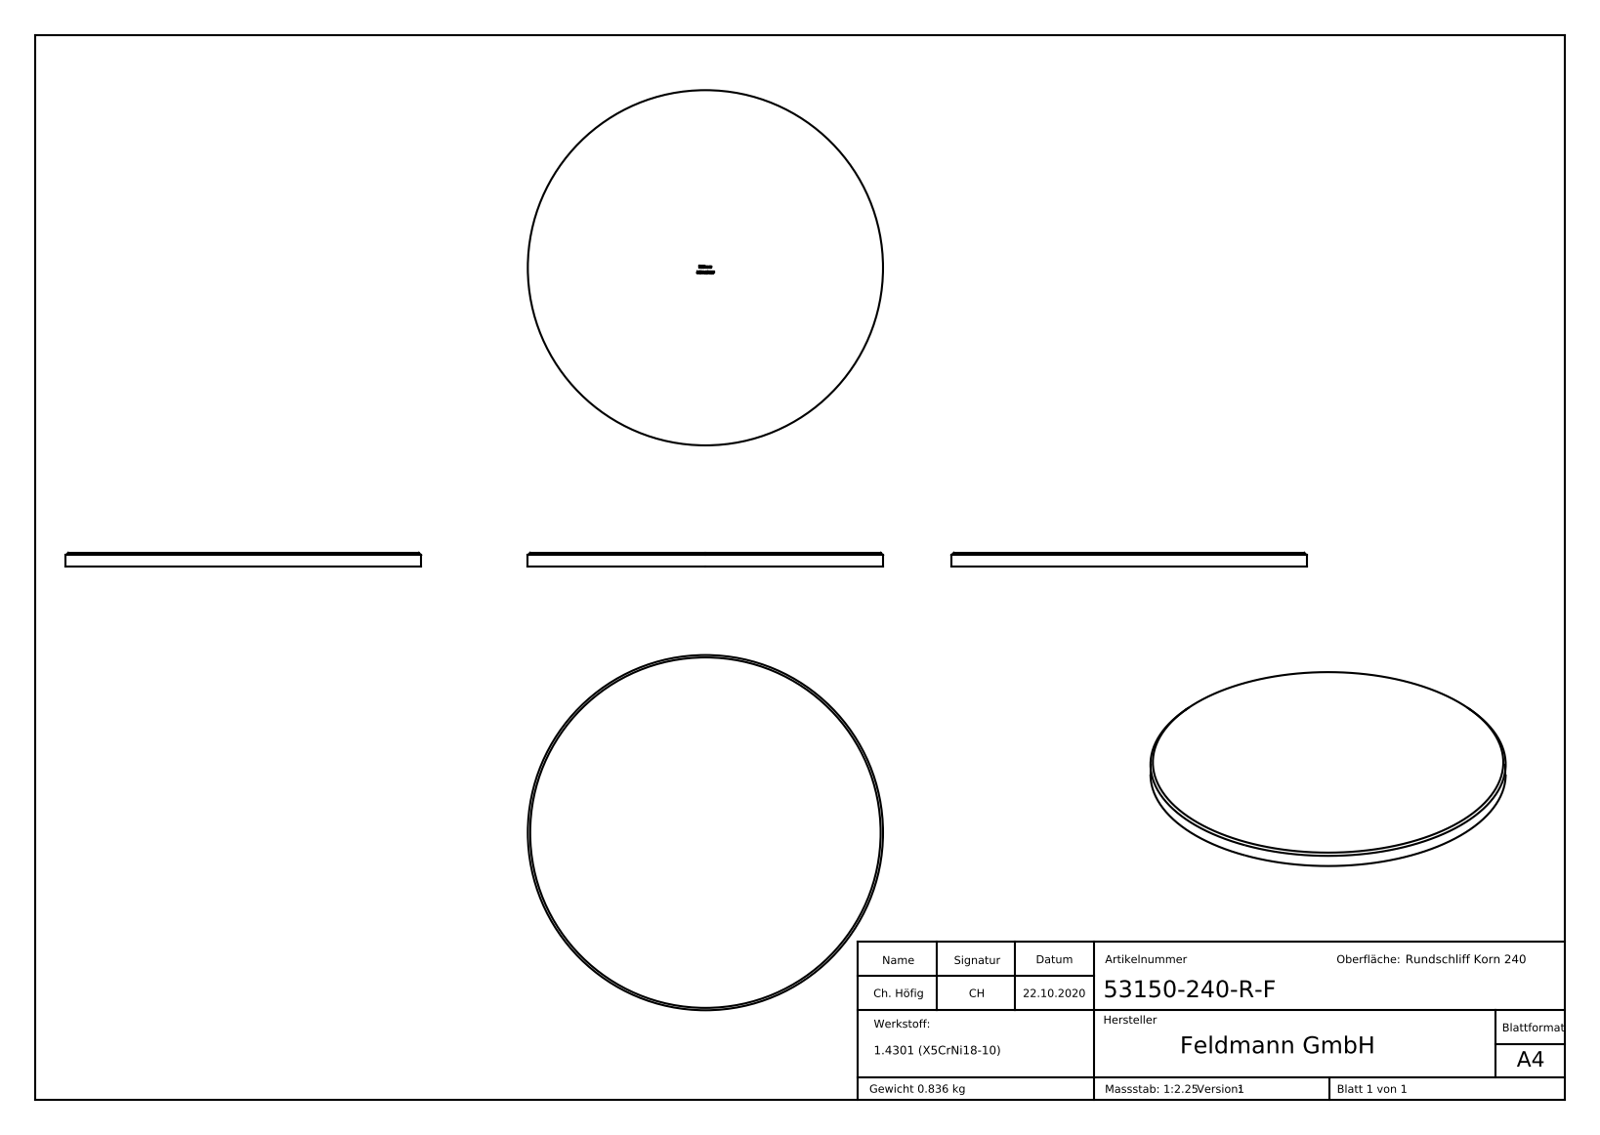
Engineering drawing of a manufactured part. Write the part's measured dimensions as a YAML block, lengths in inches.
part_name: "53150-240-R-F"
step_written_by: "SolidWorks 2018 (CONFIG_CONTROL_DESIGN)"
units: inches
bodies: {solids: 1, faces: 268, planar: 157, cylindrical: 2, other: 109}
overall_size: [5.906, 5.906, 0.236]
volume: 6.456
surface_area: 58.75
round_bosses_or_shafts:
  - {diameter: 5.906, count: 1}
face_to_face_distances: [0.236, 0.232, 0.091, 0.048, 0.031, 0.137, 0.018, 0.019, 0.07, 0.021]
